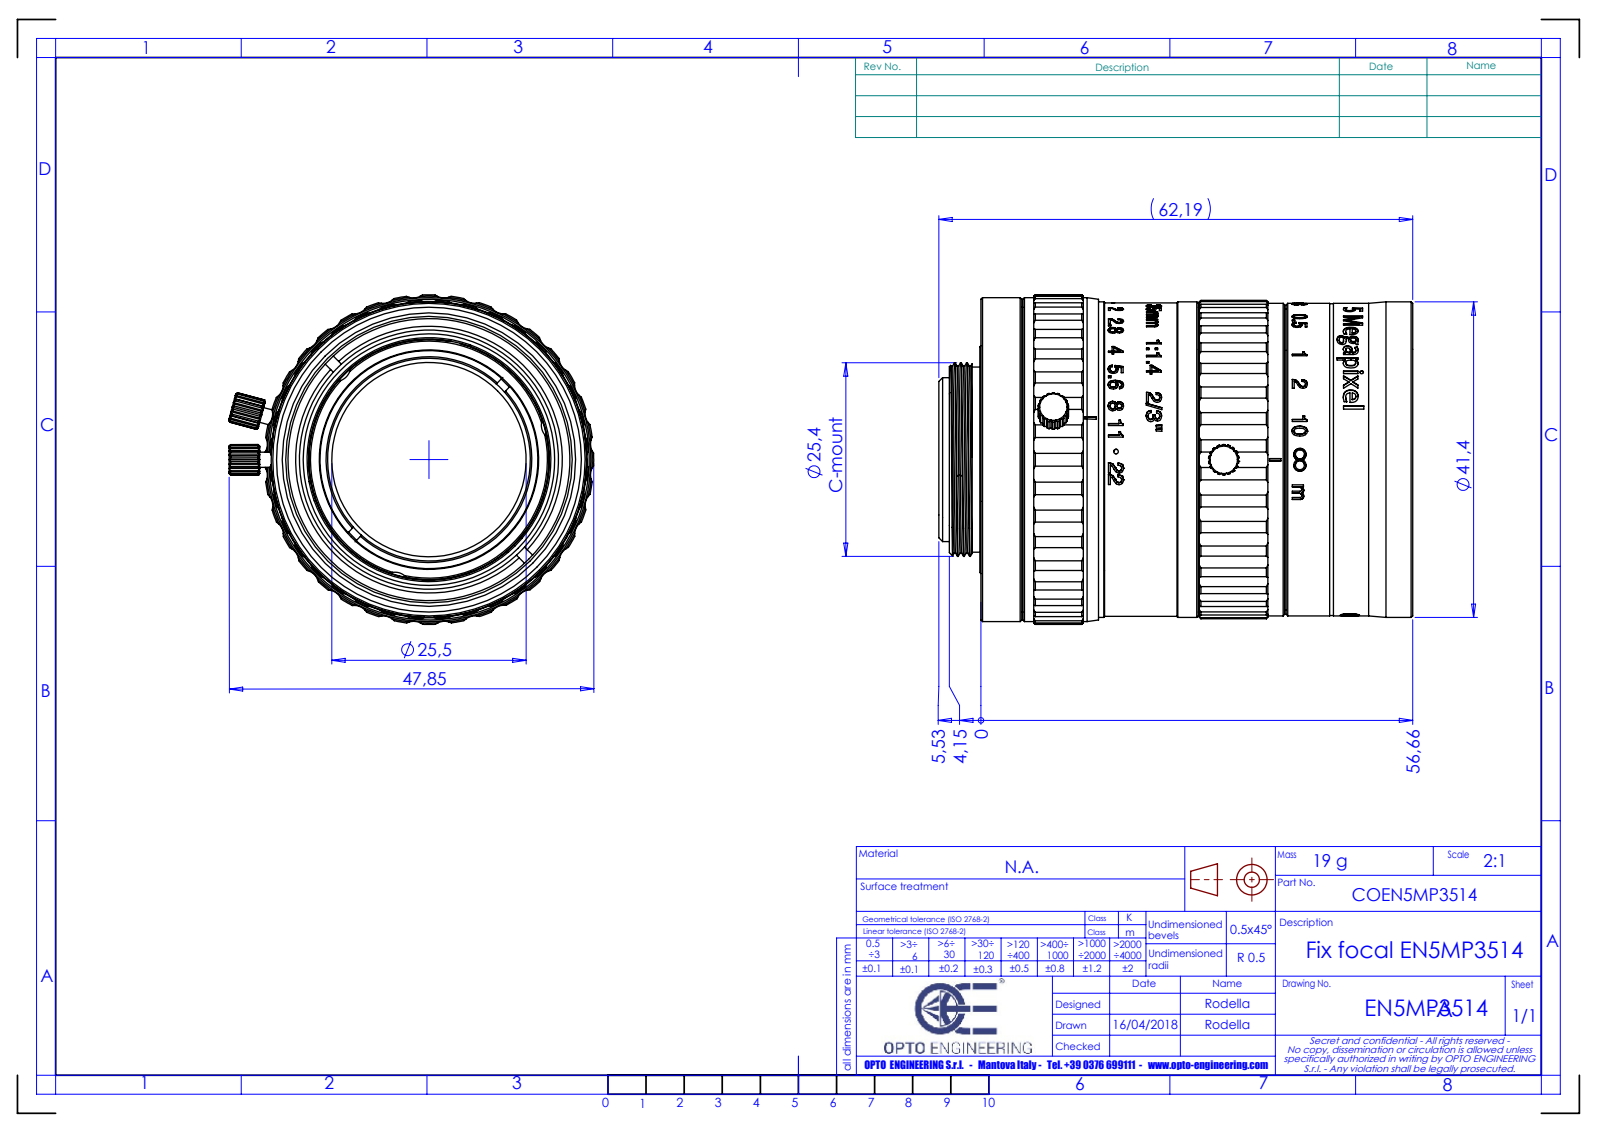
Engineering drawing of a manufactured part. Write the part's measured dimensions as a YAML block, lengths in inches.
part_name: "PRT0058; P6665A02_2_AF0; MANIFOLD_SOLID_BREP_5384; HQZ_1_ASM (+8 more)"
step_written_by: "PRO/ENGINEER BY PARAMETRIC TECHNOLOGY CORPORATION, 2011310 (AUTOMOTIVE_DESIGN)"
units: inches
bodies: {solids: 20, faces: 1977, planar: 646, cylindrical: 508, other: 823}
overall_size: [3.418, 1.969, 1.969]
volume: 5.16
surface_area: 68.27
round_holes:
  - {diameter: 0.043, count: 3}
  - {diameter: 0.055, count: 3}
  - {diameter: 0.059, count: 3}
  - {diameter: 0.071, count: 3}
  - {diameter: 0.098, count: 3}
  - {diameter: 0.102, count: 3}
  - {diameter: 0.063, count: 2}
  - {diameter: 0.551, count: 1}
  - {diameter: 0.571, count: 1}
  - {diameter: 0.63, count: 1}
  - {diameter: 0.65, count: 1}
  - {diameter: 0.846, count: 1}
round_bosses_or_shafts:
  - {diameter: 0.098, count: 3}
  - {diameter: 0.067, count: 3}
  - {diameter: 0.079, count: 2}
  - {diameter: 1.673, count: 1}
  - {diameter: 1.673, count: 1}
  - {diameter: 1.63, count: 1}
  - {diameter: 1.618, count: 1}
  - {diameter: 1.614, count: 1}
partial_cylinders:
  - {radius: 0.079, count: 83}
  - {radius: 0.012, count: 4}
  - {radius: 0.049, count: 4}
  - {radius: 0.018, count: 3}
  - {radius: 0.051, count: 3}
  - {radius: 0.039, count: 2}
  - {radius: 0.037, count: 1}
  - {radius: 0.803, count: 1}
face_to_face_distances: [1.969, 1.181, 1.651, 2.832, 1.604, 0.048, 1.229, 1.645, 0.042, 1.187]
hole_center_spacings: [0.681, 0.673, 0.689, 1.166, 1.362, 0.681, 1.193, 0.177]
